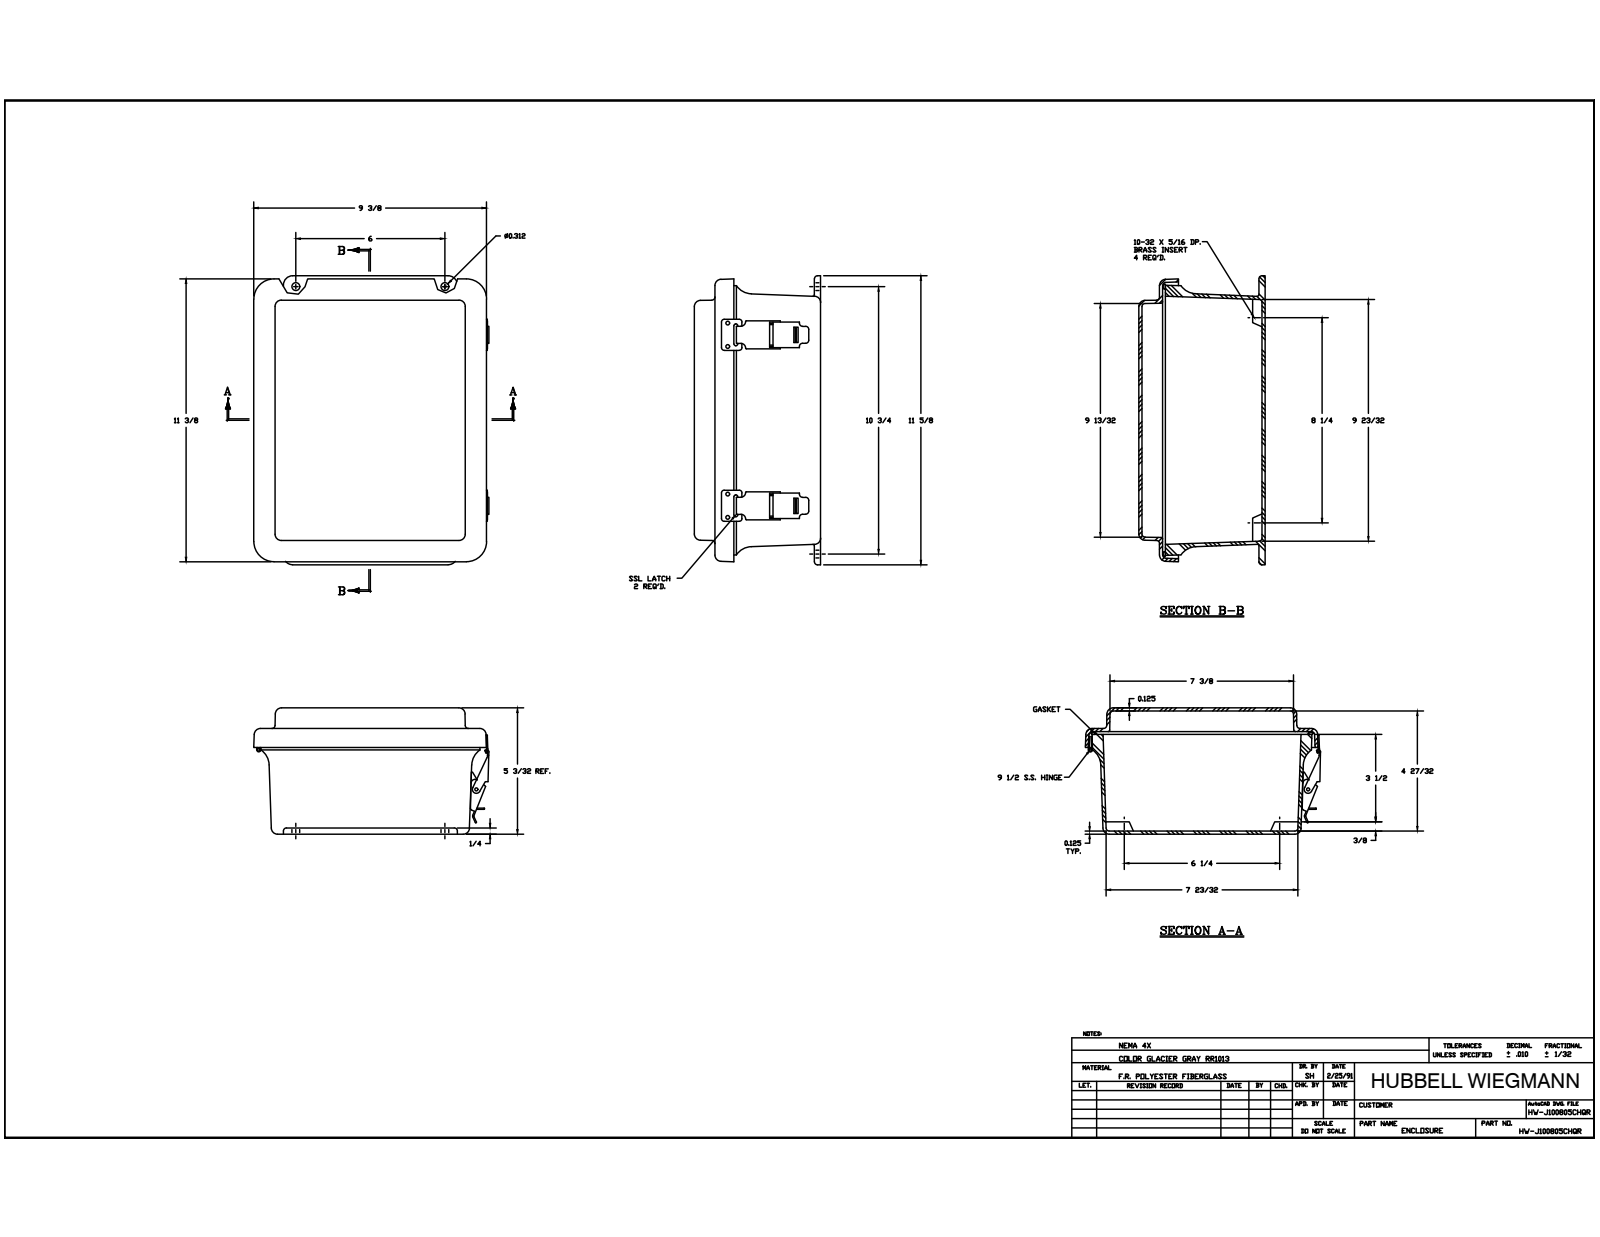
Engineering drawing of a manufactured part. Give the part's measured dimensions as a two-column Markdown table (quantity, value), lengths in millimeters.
| quantity | value |
| --- | --- |
| part name | J1008HL_3; RMINS45821P_37; RMINS45821P_38; RMINS45821P_39 (+8 more) |
| STEP written by | Autodesk Inventor 2014 (AUTOMOTIVE_DESIGN) |
| units | millimeters |
| bodies | 38 solids, 989 faces (409 planar, 409 cylindrical, 171 other) |
| overall size | 295.27 × 242.16 × 128.6 |
| volume | 1 029 000 mm³ |
| surface area | 570 464 mm² |
| round holes (diameter × count) | 3.56 × 20, 2.64 × 8, 3.33 × 8, 3.86 × 5, 3.3 × 4, 3.96 × 4, 5.54 × 4, 3.43 × 2, 9.52 × 2, 2.16 × 1, 2.16 × 1 |
| round bosses / shafts (diameter × count) | 3.17 × 16, 6.35 × 8, 6.86 × 4, 7.62 × 1, 4.31 × 1, 3.94 × 1, 3.05 × 1 |
| partial cylindrical surfaces (radius × count) | 3.17 × 32, 0.38 × 20, 0.79 × 20, 1.14 × 16, 0.76 × 12, 6.35 × 12, 0.57 × 9, 1.52 × 6 |
| main face-to-face distances | 3.17, 3.18, 122.25, 125.42, 128.6, 125.43, 104.36, 101.19, 21.06, 24.24 |
| hole center spacings | 177.8, 19.05, 178.82, 23.81, 152.4, 76.2, 6.35, 37.27 |
